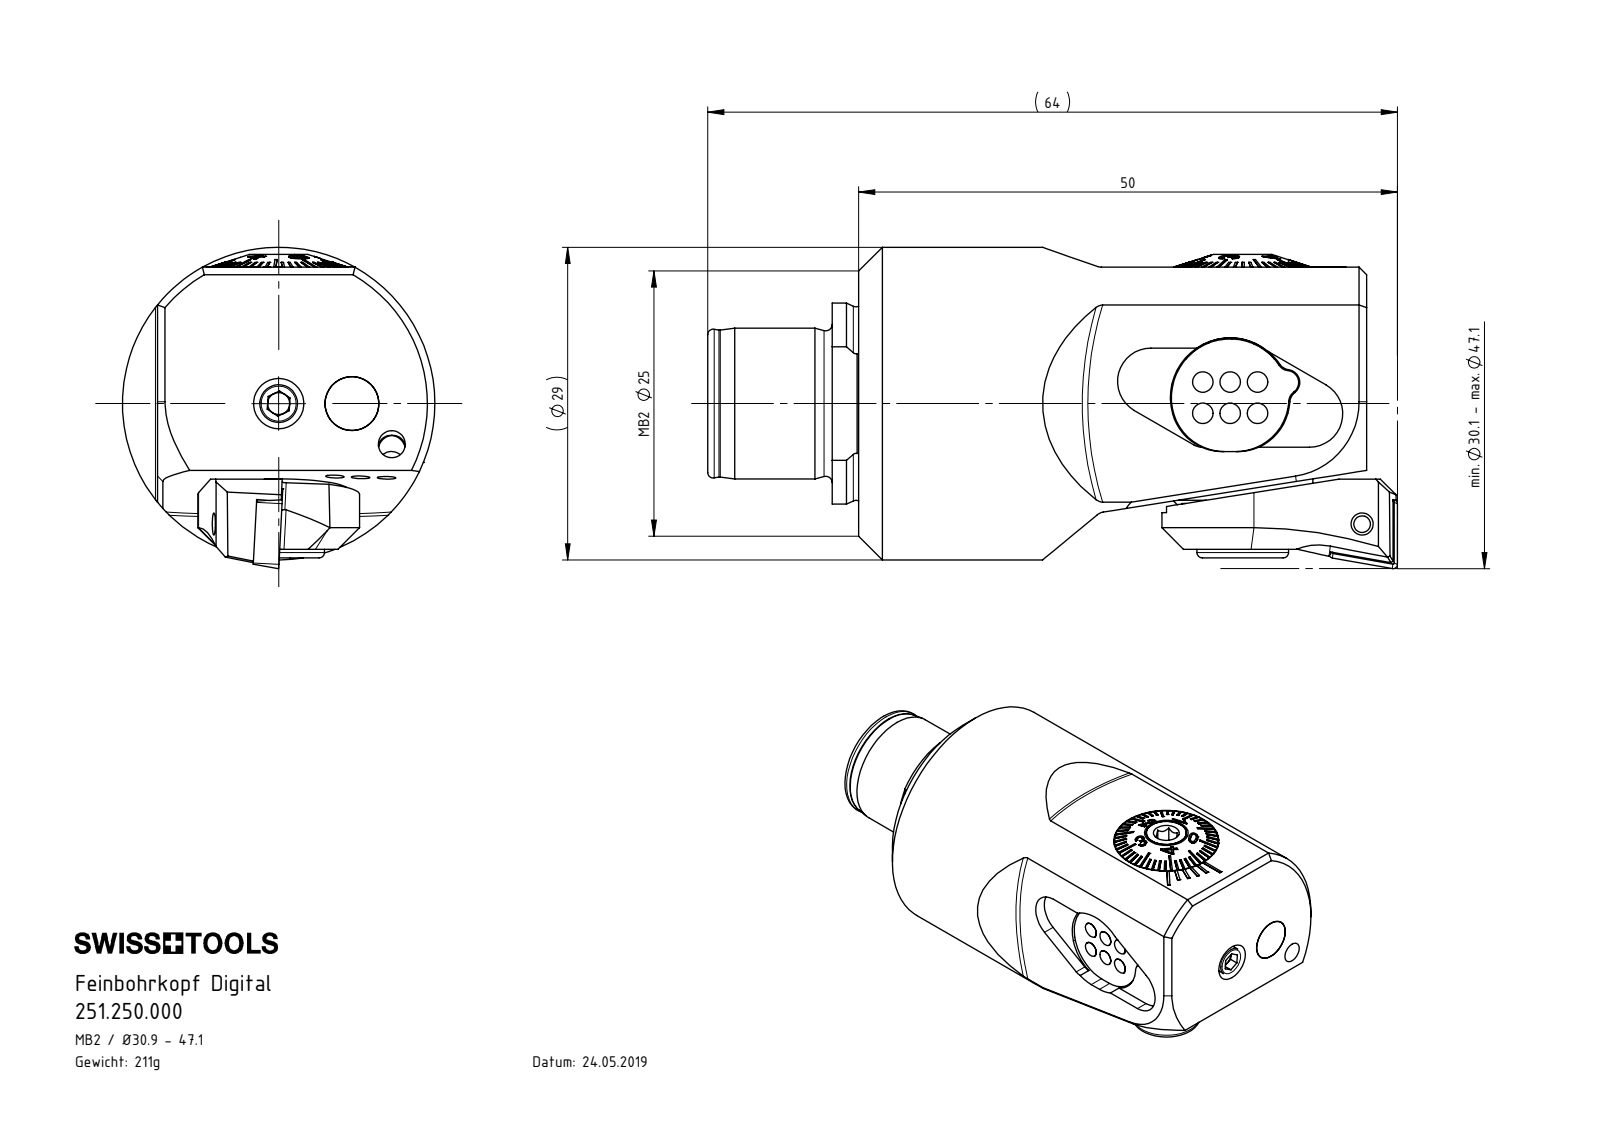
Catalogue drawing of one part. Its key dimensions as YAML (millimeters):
part_name: "251.250.000; Klebstoff D5; PEE-DA1.011.026_A; T7 M2.5 x 6_PreviewCfg (+8 more)"
step_written_by: "SolidWorks 2017 (CONFIG_CONTROL_DESIGN)"
units: millimeters
bodies: {solids: 20, faces: 908, planar: 398, cylindrical: 190, other: 320}
overall_size: [64, 27.7, 25]
volume: 22993
surface_area: 12461
round_holes:
  - {diameter: 2, count: 4}
  - {diameter: 2.05, count: 3}
  - {diameter: 4.2, count: 3}
  - {diameter: 5, count: 2}
  - {diameter: 0.7, count: 1}
  - {diameter: 2.1, count: 1}
  - {diameter: 2.4, count: 1}
  - {diameter: 2.7, count: 1}
  - {diameter: 2.8, count: 1}
  - {diameter: 3, count: 1}
  - {diameter: 3.85, count: 1}
  - {diameter: 5.5, count: 1}
round_bosses_or_shafts:
  - {diameter: 1.9, count: 6}
  - {diameter: 5, count: 2}
  - {diameter: 4.95, count: 2}
  - {diameter: 2.5, count: 2}
  - {diameter: 25, count: 1}
  - {diameter: 14, count: 1}
  - {diameter: 12.98, count: 1}
  - {diameter: 12.85, count: 1}
partial_cylinders:
  - {radius: 0.21, count: 6}
  - {radius: 0.36, count: 5}
  - {radius: 0.5, count: 4}
  - {radius: 1.1, count: 3}
  - {radius: 1.2, count: 3}
  - {radius: 1.32, count: 2}
  - {radius: 1.4, count: 2}
  - {radius: 3.1, count: 2}
face_to_face_distances: [1.5, 4.25, 19.95, 0.8, 3.1, 3.9, 19.6, 15.7, 47.15, 2.3]
hole_center_spacings: [2.6, 0.68, 3.84, 3.99, 4.48, 6.8, 9.46, 16.5]
